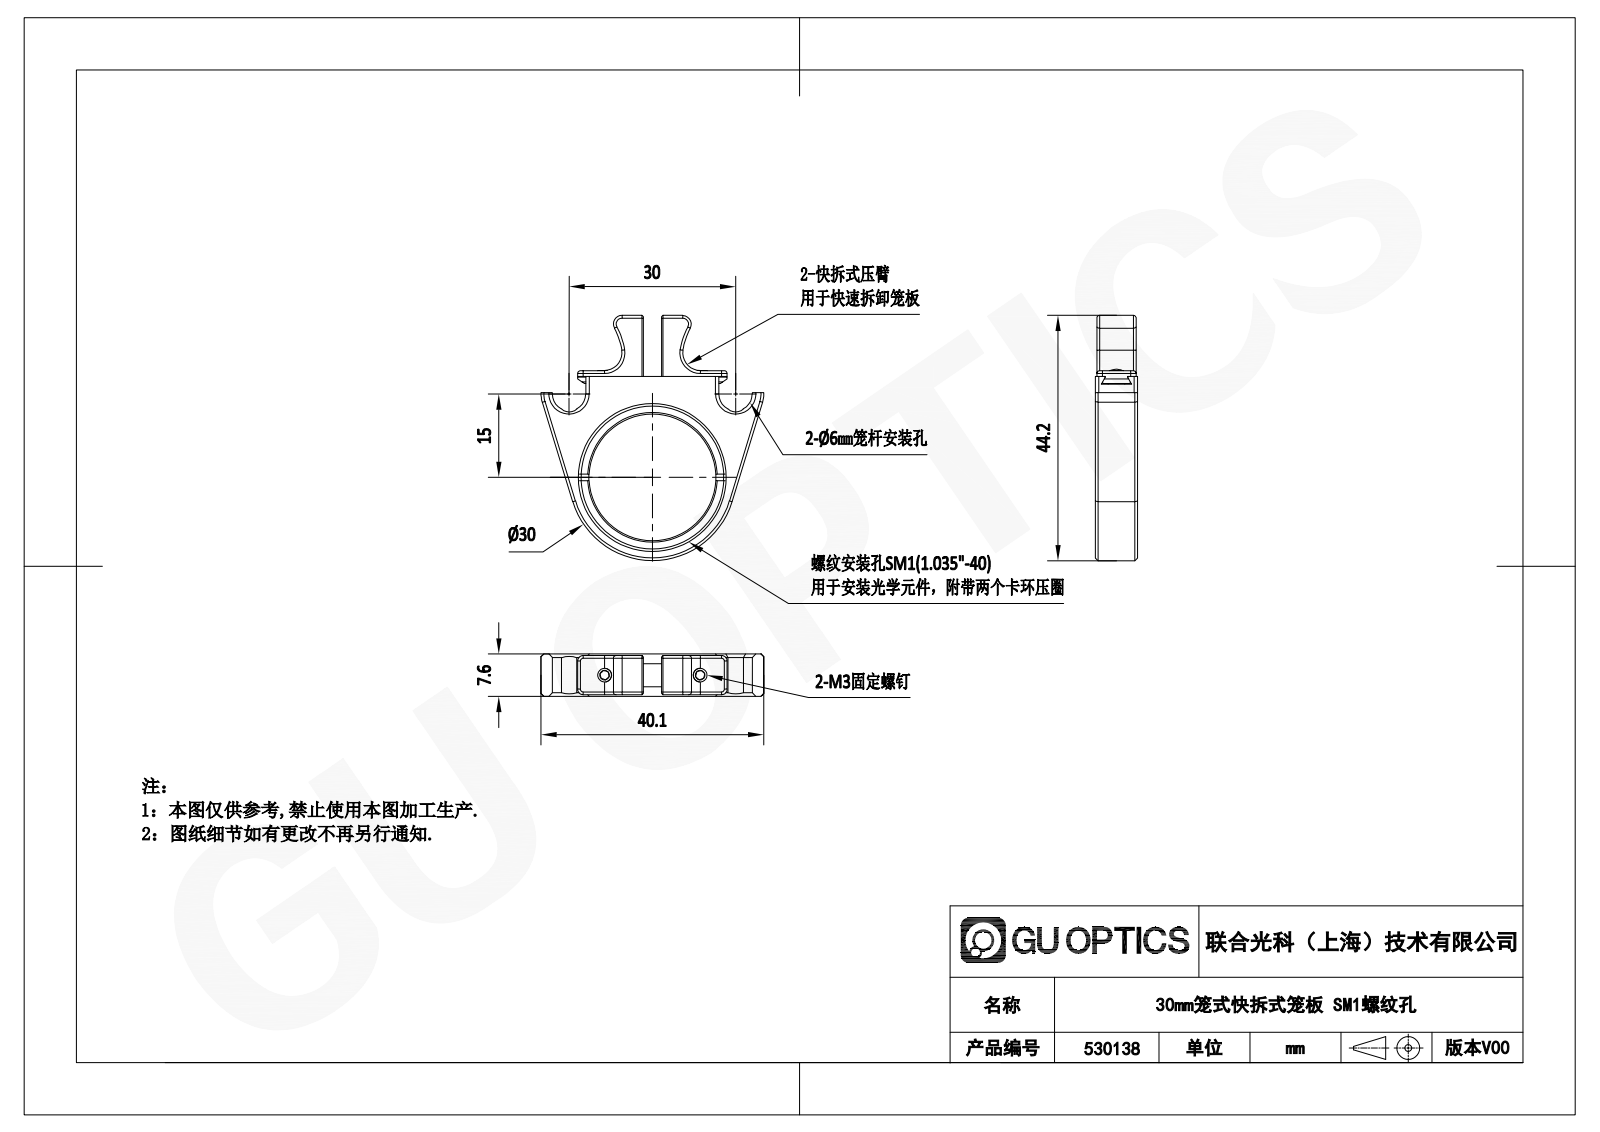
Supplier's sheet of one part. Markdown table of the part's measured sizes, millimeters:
| quantity | value |
| --- | --- |
| part name | 530138 |
| STEP written by | SolidWorks 2020 (CONFIG_CONTROL_DESIGN) |
| units | millimeters |
| bodies | 0 solids, 180 faces (94 planar, 38 cylindrical, 48 other) |
| overall size | 44.2 × 40.1 × 7.62 |
| round holes (diameter × count) | 25.65 × 1 |
| round bosses / shafts (diameter × count) | 3.18 × 2, 2.5 × 2, 22.9 × 1 |
| partial cylindrical surfaces (radius × count) | 0.5 × 6, 1 × 4, 1.57 × 2, 1.98 × 2, 3.01 × 2, 3.17 × 2, 5.05 × 2, 12.7 × 2 |
| main face-to-face distances | 7.62, 2, 5.62, 7.34, 1.72, 5.34, 1.4, 1.27, 3.62, 7.06 |
